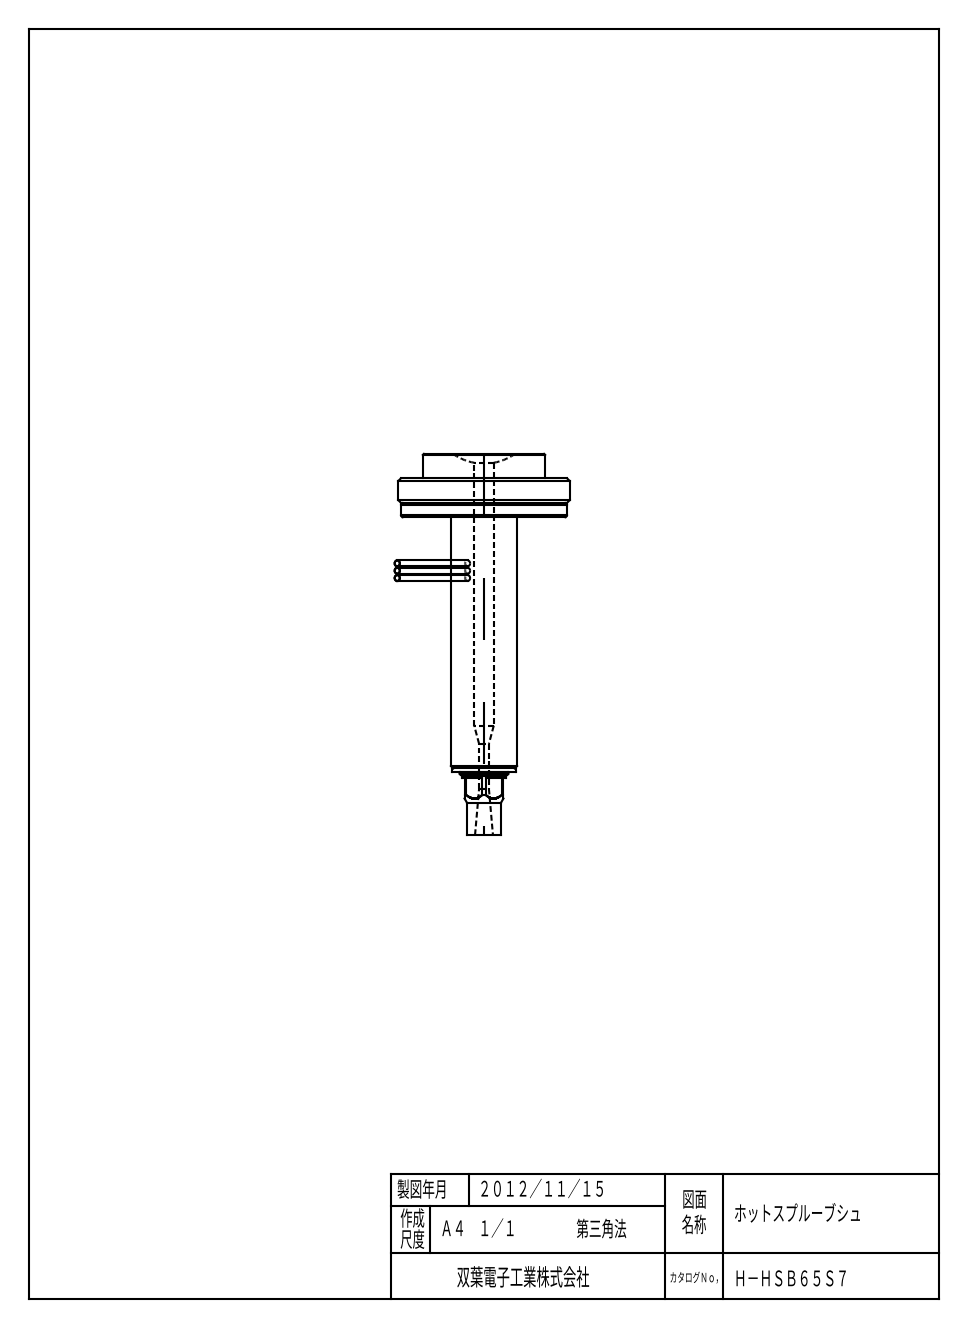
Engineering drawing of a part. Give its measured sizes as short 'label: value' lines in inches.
name: HSB65S7
written by: SIEMENS PLM Software NX 2023 (AUTOMOTIVE_DESIGN)
unit: in
bodies: 1 solid, 79 faces (23 planar, 30 cylindrical, 26 other)
size: 6.313 × 6.313 × 3.071
volume: 1.027 in³; area: 13.8 in²
holes: 4× ⌀0.217, 4× ⌀0.35, 1× ⌀0.157, 1× ⌀0.63
bosses: 3× ⌀0.157, 3× ⌀0.047, 1× ⌀1.378, 1× ⌀1.339, 1× ⌀0.531, 1× ⌀0.512, 1× ⌀0.394, 1× ⌀0.393
rounds: 1× R0.492
face distances: 0.197, 0.315, 0.512, 0.02, 0.295, 0.217, 0.118, 0.098, 2.05, 2.246
hole spacings: 0.492, 0.696, 0.984
